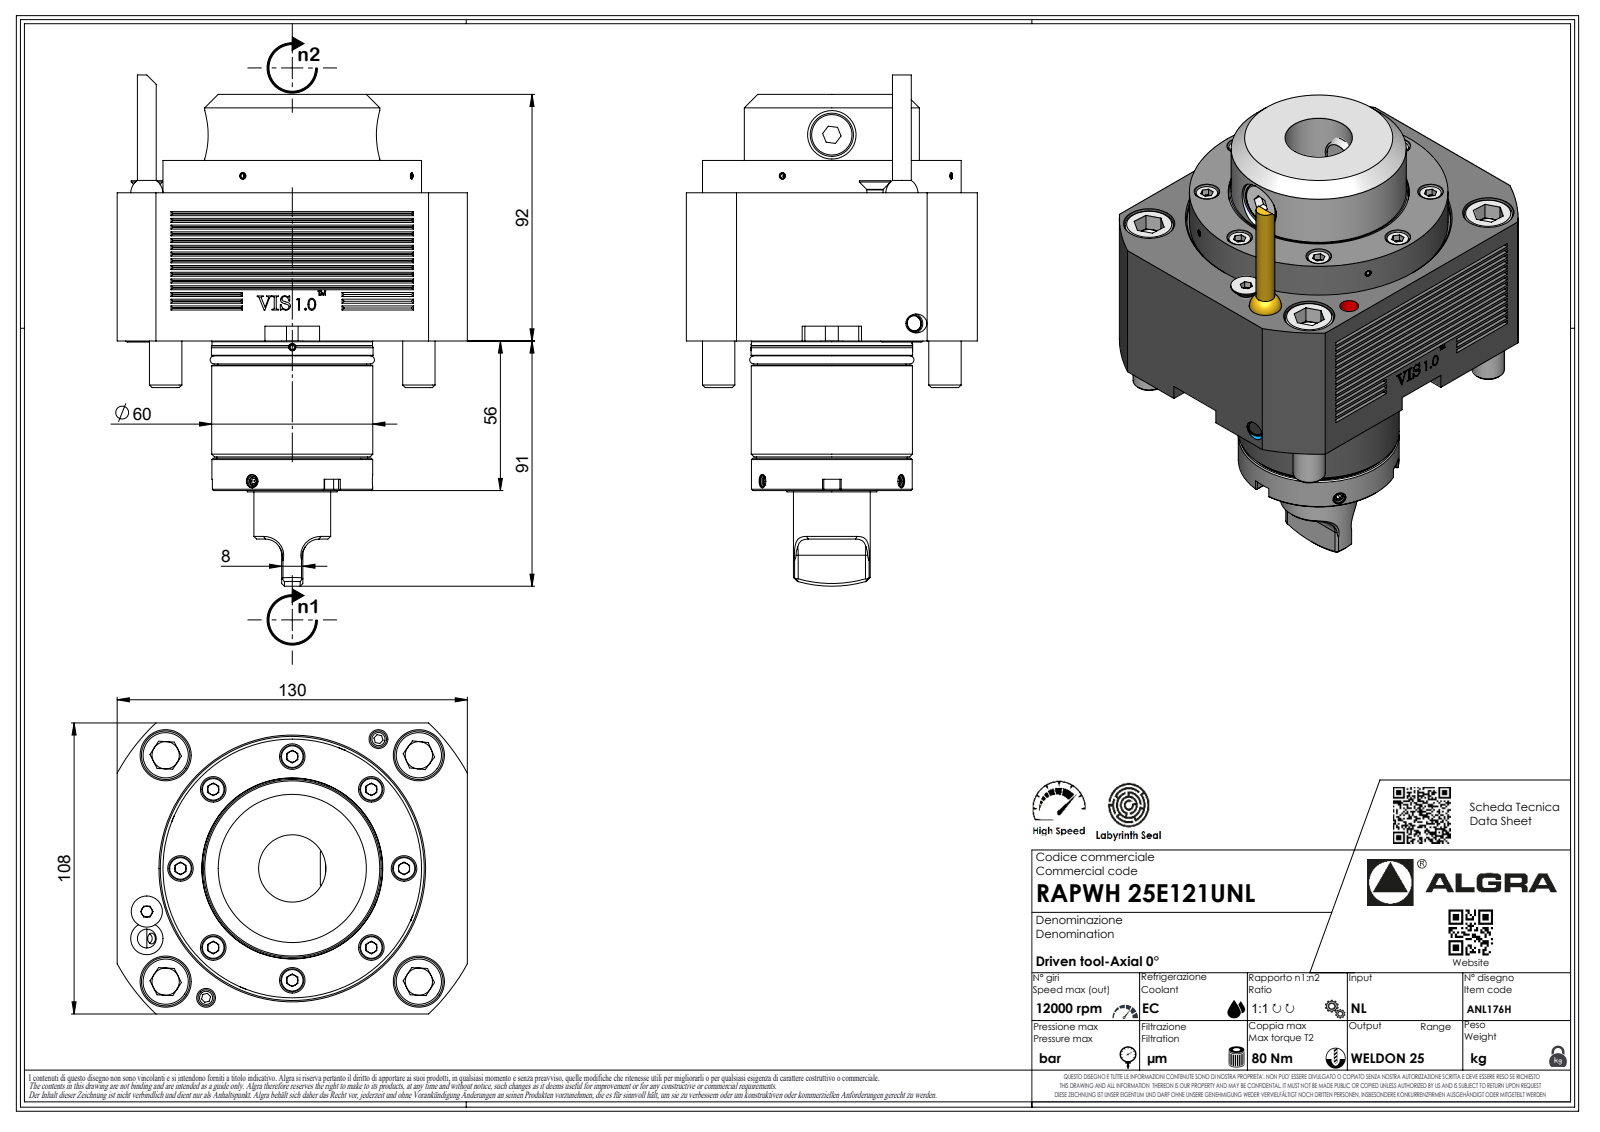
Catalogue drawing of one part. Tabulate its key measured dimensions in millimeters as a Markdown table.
| quantity | value |
| --- | --- |
| part name | RAPWH25E121UNL |
| STEP written by | SolidWorks 2023 (AUTOMOTIVE_DESIGN) |
| units | millimeters |
| bodies | 1 solid, 397 faces (269 planar, 56 cylindrical, 72 other) |
| overall size | 189.7 × 130 × 108 |
| volume | 1 085 000 mm³ |
| surface area | 76 666 mm² |
| round holes (diameter × count) | 2.1 × 1, 4 × 1 |
| round bosses / shafts (diameter × count) | 12 × 4, 96 × 1, 65 × 1, 60 × 1, 28.5 × 1, 7 × 1, 6.37 × 1, 1.7 × 1 |
| partial cylindrical surfaces (radius × count) | 8 × 8, 0.33 × 7, 0.52 × 7, 3.7 × 7, 6 × 6, 0.21 × 1, 2 × 1, 46 × 1 |
| main face-to-face distances | 55, 108, 67, 12, 130, 91.5, 36.5, 24.5, 55.5, 110.5 |
